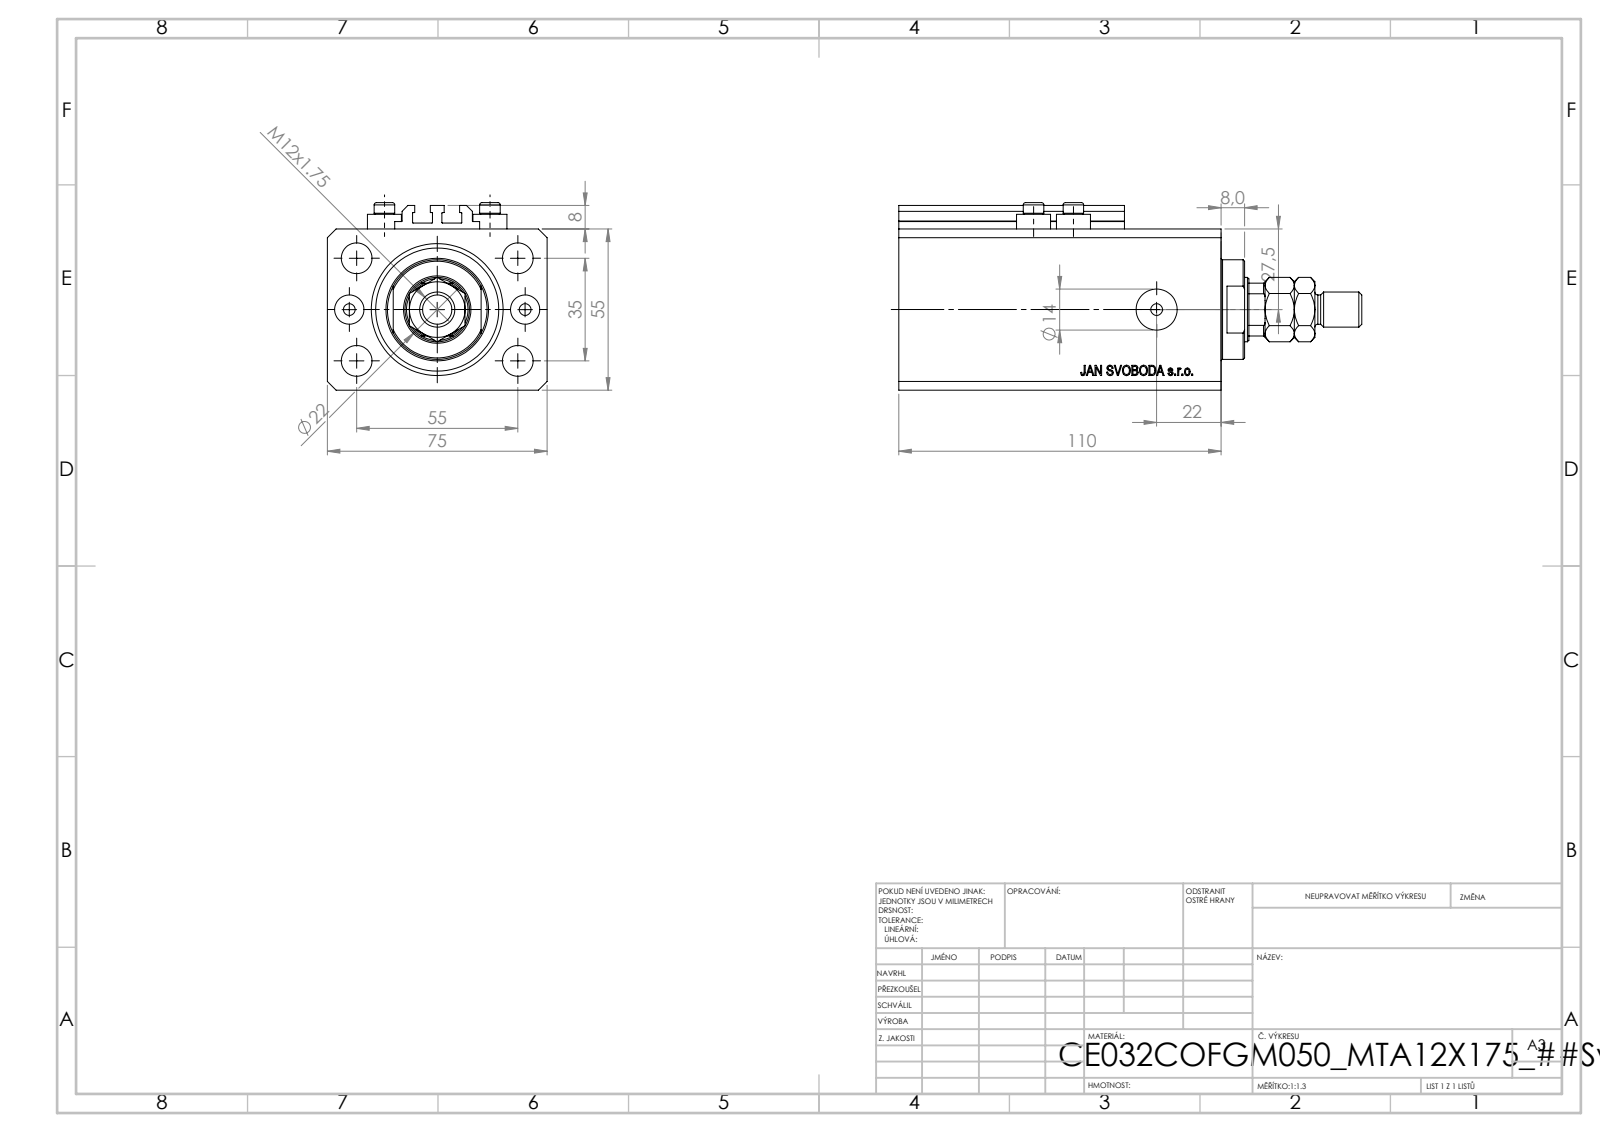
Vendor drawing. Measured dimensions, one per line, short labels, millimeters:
name: MTA; V250CE_C_VCP; V250CE_C_Body; V250CE_VC_C (+1 more)
written by: SolidWorks 2019 (CONFIG_CONTROL_DESIGN)
unit: mm
bodies: 9 solids, 1083 faces (519 planar, 90 cylindrical, 474 other)
size: 158 × 75 × 64
volume: 415 906 mm³; area: 93 435 mm²
holes: 8× ⌀4, 5× ⌀10.5, 2× ⌀10, 2× ⌀14, 1× ⌀22, 1× ⌀32, 1× ⌀45
bosses: 4× ⌀11.6, 4× ⌀7, 1× ⌀34, 1× ⌀12, 1× ⌀10
rounds: 10× R0.2, 1× R10.5
face distances: 55, 75, 15, 110, 95, 9.9, 85.1, 100.1, 2.5, 3
hole spacings: 17.68, 32.6, 60.1, 13.6, 30, 35, 36, 38.48
